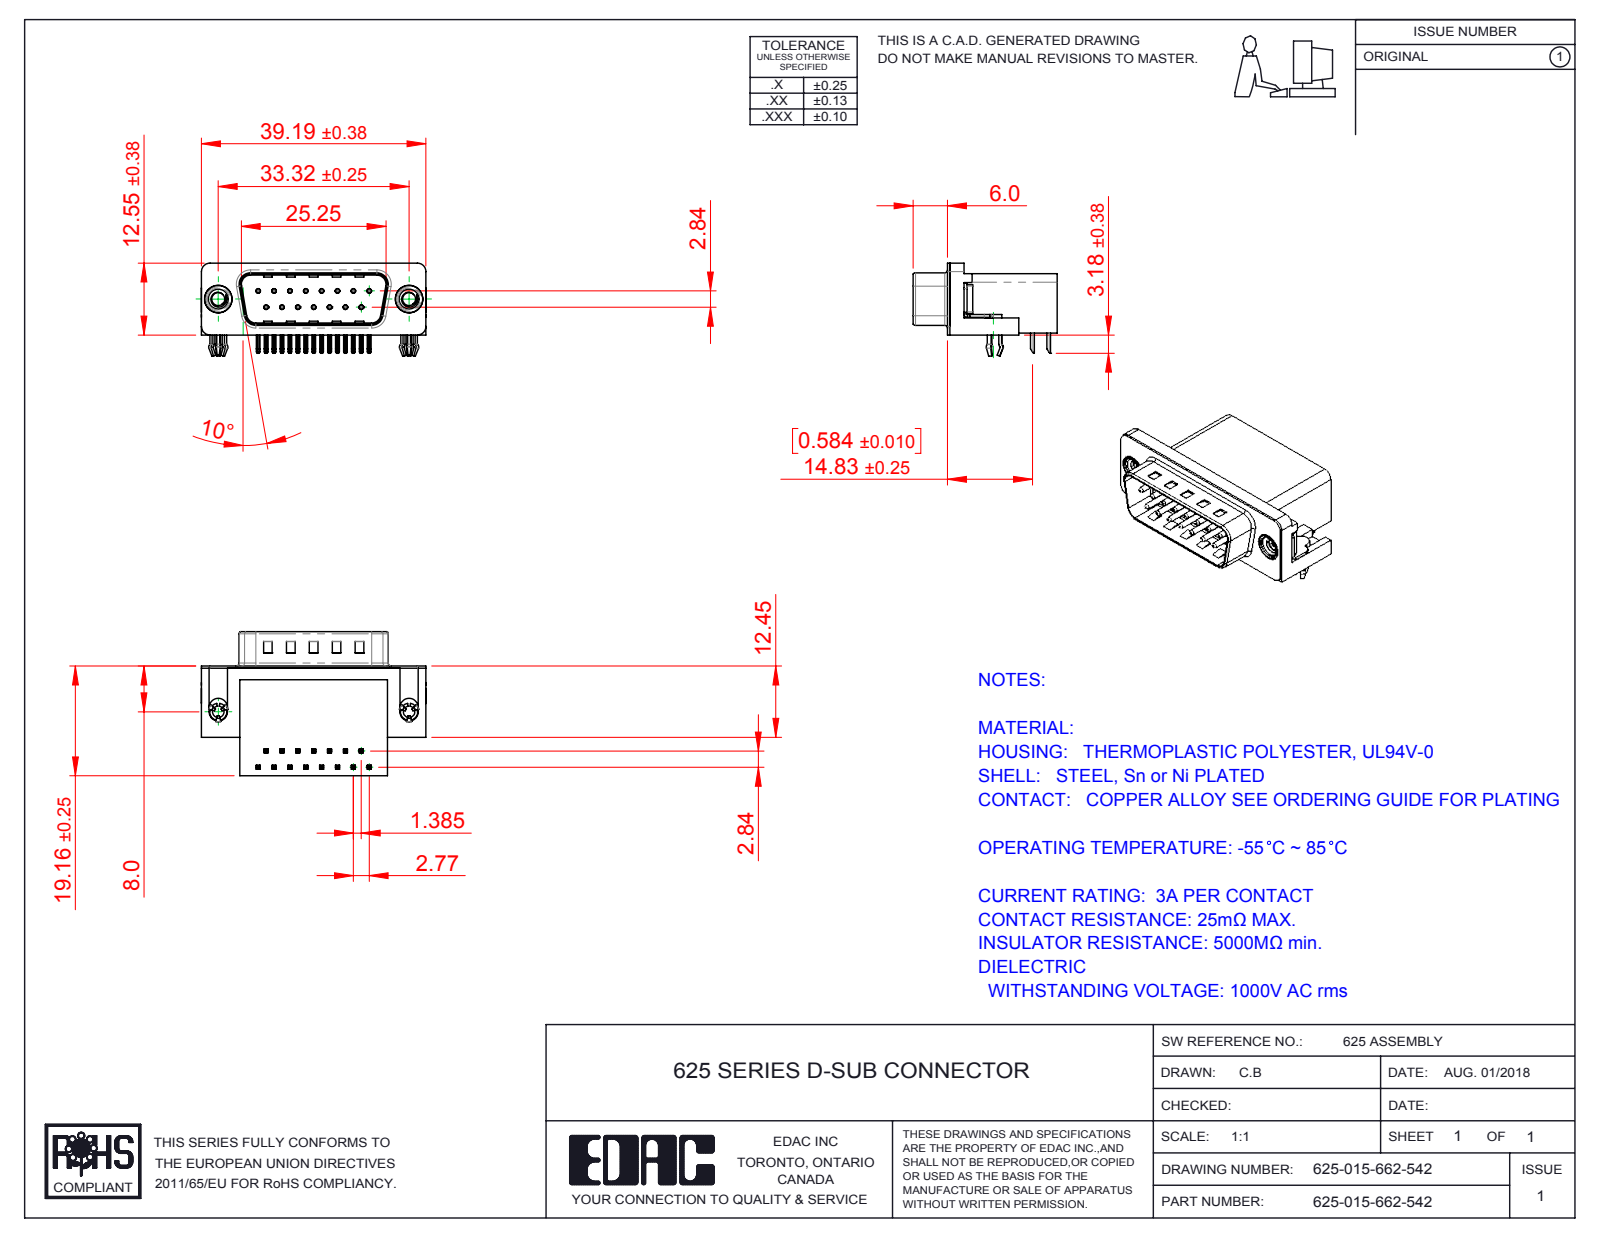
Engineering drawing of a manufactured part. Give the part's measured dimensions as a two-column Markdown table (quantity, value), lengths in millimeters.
| quantity | value |
| --- | --- |
| part name | 625 Housing_15 Socket; 625 4-40 Threaded Rivet; 625 Contact Top; 625-015-662-542 (+3 more) |
| STEP written by | SolidWorks 2016 (CONFIG_CONTROL_DESIGN) |
| units | millimeters |
| bodies | 21 solids, 1583 faces (931 planar, 453 cylindrical, 199 other) |
| overall size | 39.22 × 25.16 × 16.25 |
| volume | 6 253 mm³ |
| surface area | 6 486 mm² |
| round holes (diameter × count) | 0.35 × 15, 0.8 × 15, 2 × 2, 2.26 × 2, 4 × 2, 4.8 × 2, 5 × 2 |
| round bosses / shafts (diameter × count) | 0.75 × 15, 4.9 × 2, 4.75 × 2, 3.9 × 2, 3 × 2 |
| partial cylindrical surfaces (radius × count) | 0.25 × 72, 0.12 × 30, 1 × 16, 0.5 × 9, 1.6 × 8, 1.5 × 6, 0.9 × 4, 2 × 4 |
| main face-to-face distances | 0.4, 10.35, 18.76, 2.1, 10.46, 19.16, 1.7, 10.86, 8.76, 16.26 |
| hole center spacings | 3.16, 2.77, 5.54, 8.31, 11.08, 5.03, 5.04, 7.48 |
